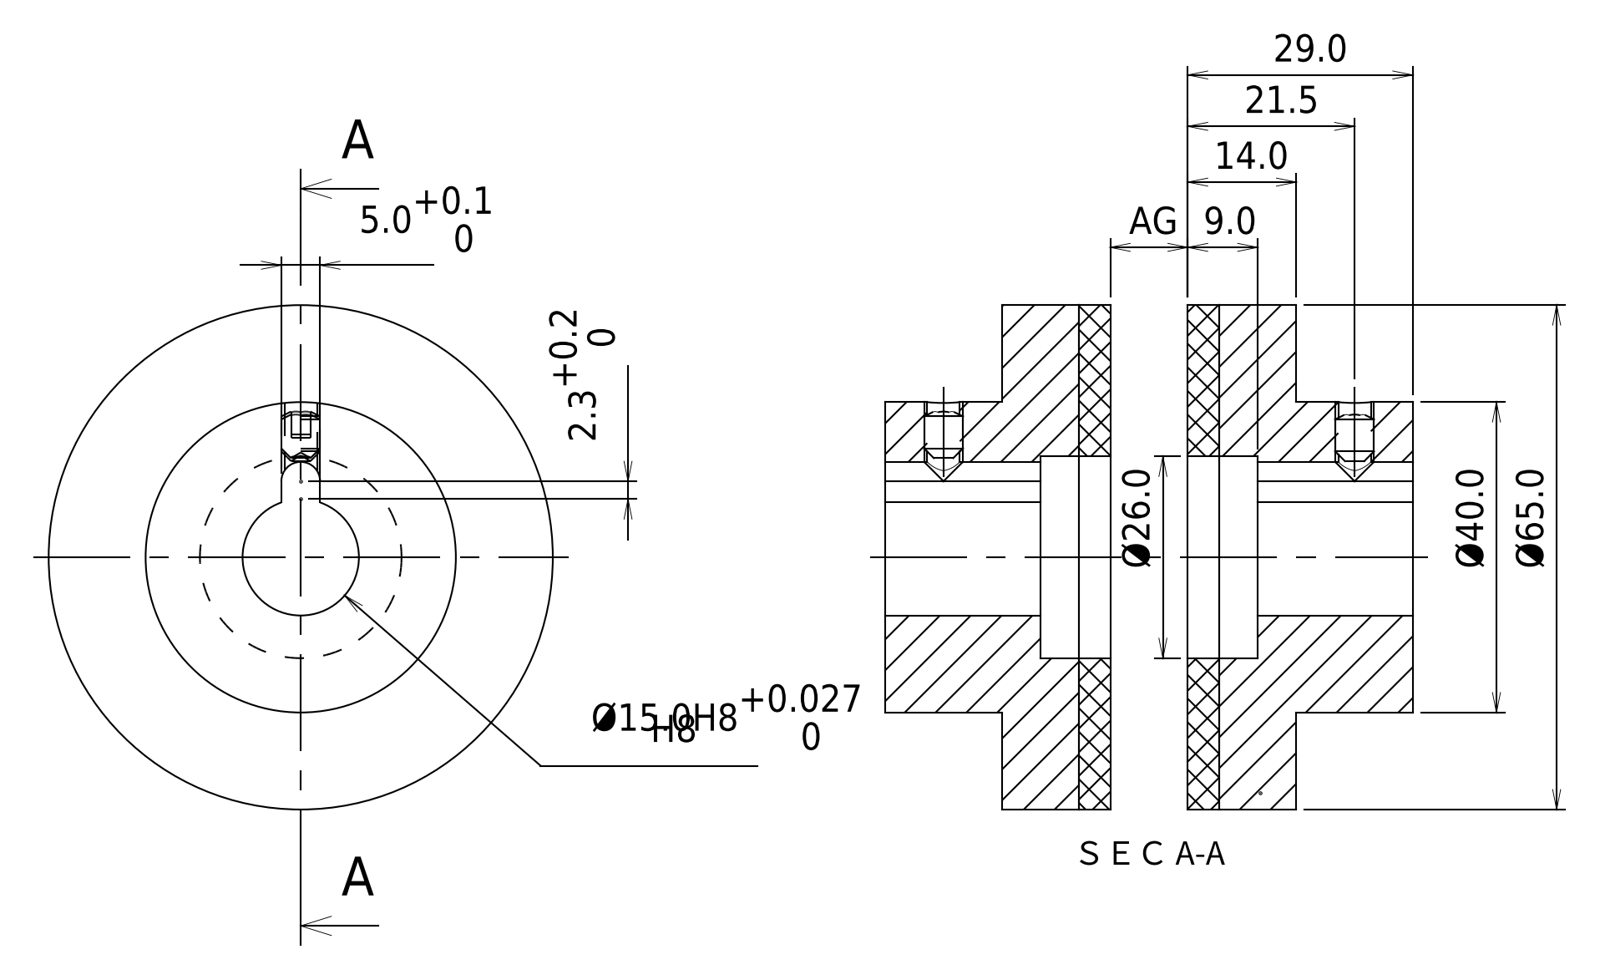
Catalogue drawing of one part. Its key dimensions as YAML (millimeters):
step_written_by: "PSStep 10.0 (CONFIG_CONTROL_DESIGN)"
units: millimeters
bodies: {solids: 4, faces: 38, planar: 22, cylindrical: 10, other: 6}
overall_size: [65, 65, 29]
volume: 56613
surface_area: 18755
round_holes:
  - {diameter: 4.2, count: 1}
  - {diameter: 15, count: 1}
  - {diameter: 26, count: 1}
round_bosses_or_shafts:
  - {diameter: 65, count: 1}
  - {diameter: 40, count: 1}
  - {diameter: 5, count: 1}
partial_cylinders:
  - {radius: 2.5, count: 1}
face_to_face_distances: [4, 14, 10, 29, 25, 15, 5, 9, 20, 2.5]
